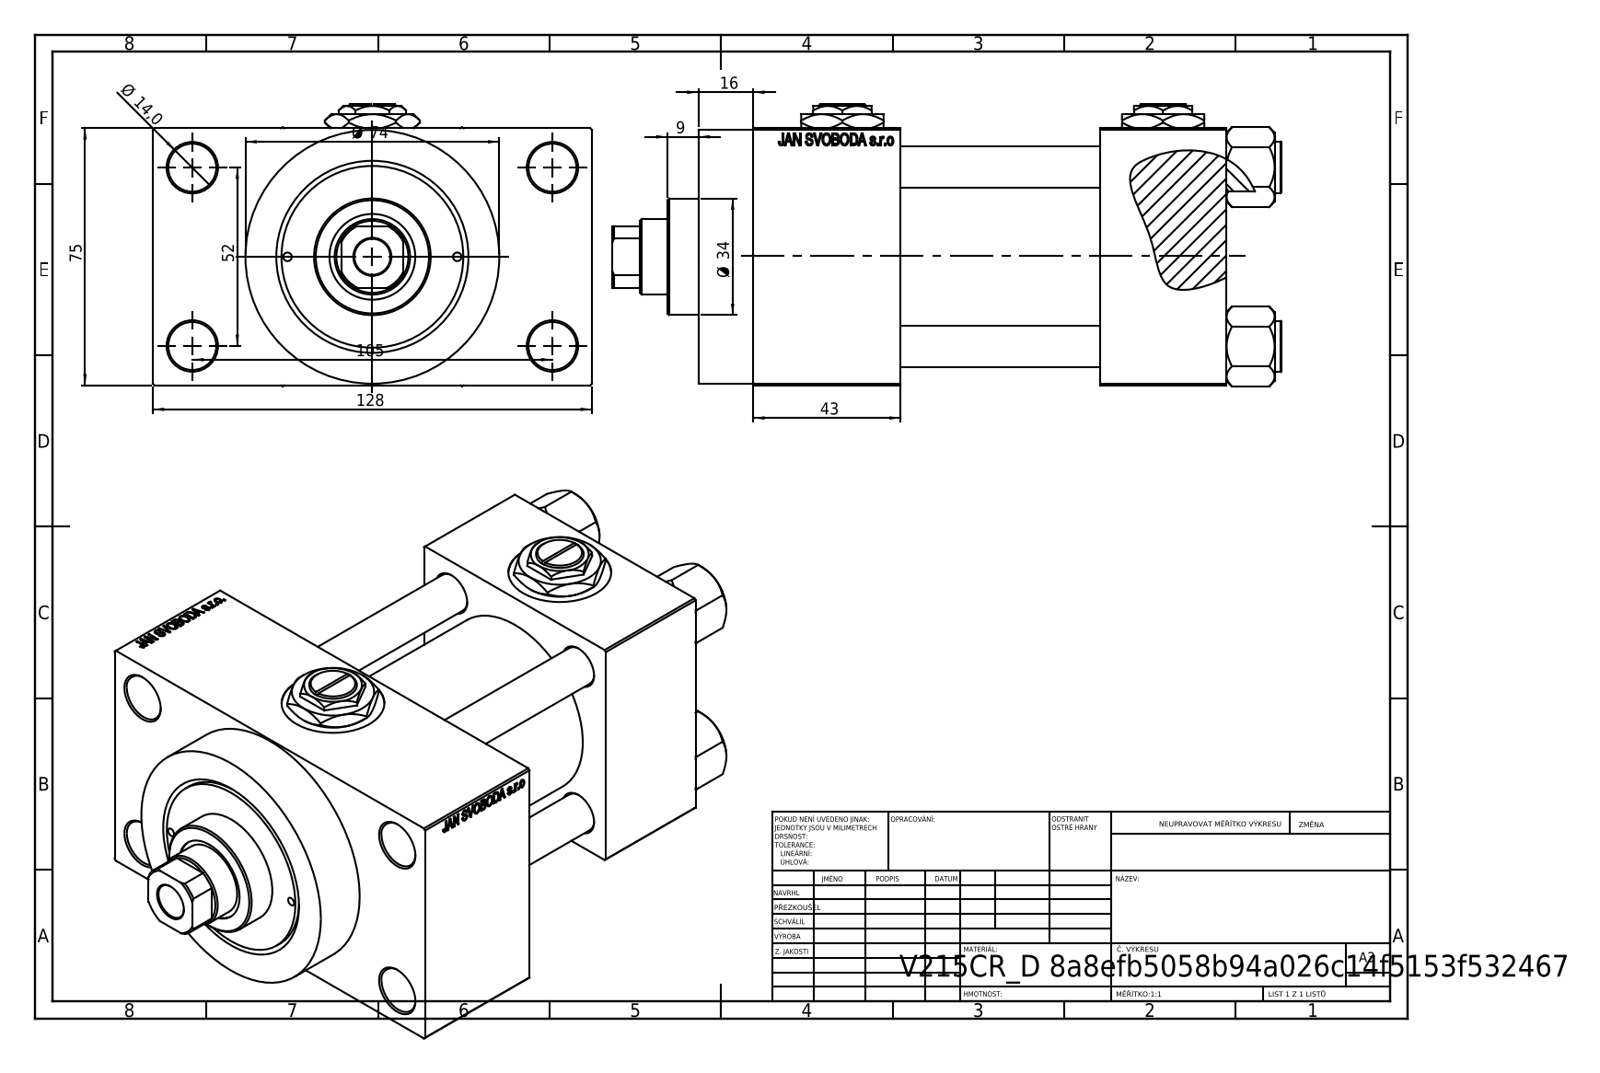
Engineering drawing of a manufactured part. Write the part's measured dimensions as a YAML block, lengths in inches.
part_name: "Zatka_pro_OIL_PORT; V215CR_VCP_D; NUT_M5_D; V215CR_D_TYCINKA (+2 more)"
step_written_by: "SolidWorks 2019 (CONFIG_CONTROL_DESIGN)"
units: inches
bodies: {solids: 13, faces: 1213, planar: 547, cylindrical: 104, other: 562}
overall_size: [7.677, 5.039, 3.239]
volume: 48.94
surface_area: 262.1
round_holes:
  - {diameter: 0.472, count: 4}
  - {diameter: 0.551, count: 4}
  - {diameter: 0.098, count: 2}
  - {diameter: 0.276, count: 2}
  - {diameter: 0.825, count: 2}
  - {diameter: 1.181, count: 2}
  - {diameter: 0.413, count: 1}
  - {diameter: 0.866, count: 1}
  - {diameter: 0.984, count: 1}
  - {diameter: 1.614, count: 1}
  - {diameter: 1.969, count: 1}
  - {diameter: 2.087, count: 1}
round_bosses_or_shafts:
  - {diameter: 0.591, count: 4}
  - {diameter: 2.913, count: 1}
  - {diameter: 2.205, count: 1}
  - {diameter: 1.339, count: 1}
partial_cylinders:
  - {radius: 0.413, count: 1}
face_to_face_distances: [2.953, 2.283, 1.457, 3.74, 1.043, 3.996, 5.433, 3.976, 1.693, 0.63]
hole_center_spacings: [1.031, 1.037, 1.456, 1.497, 2.059, 2.253, 2.3, 2.307]
